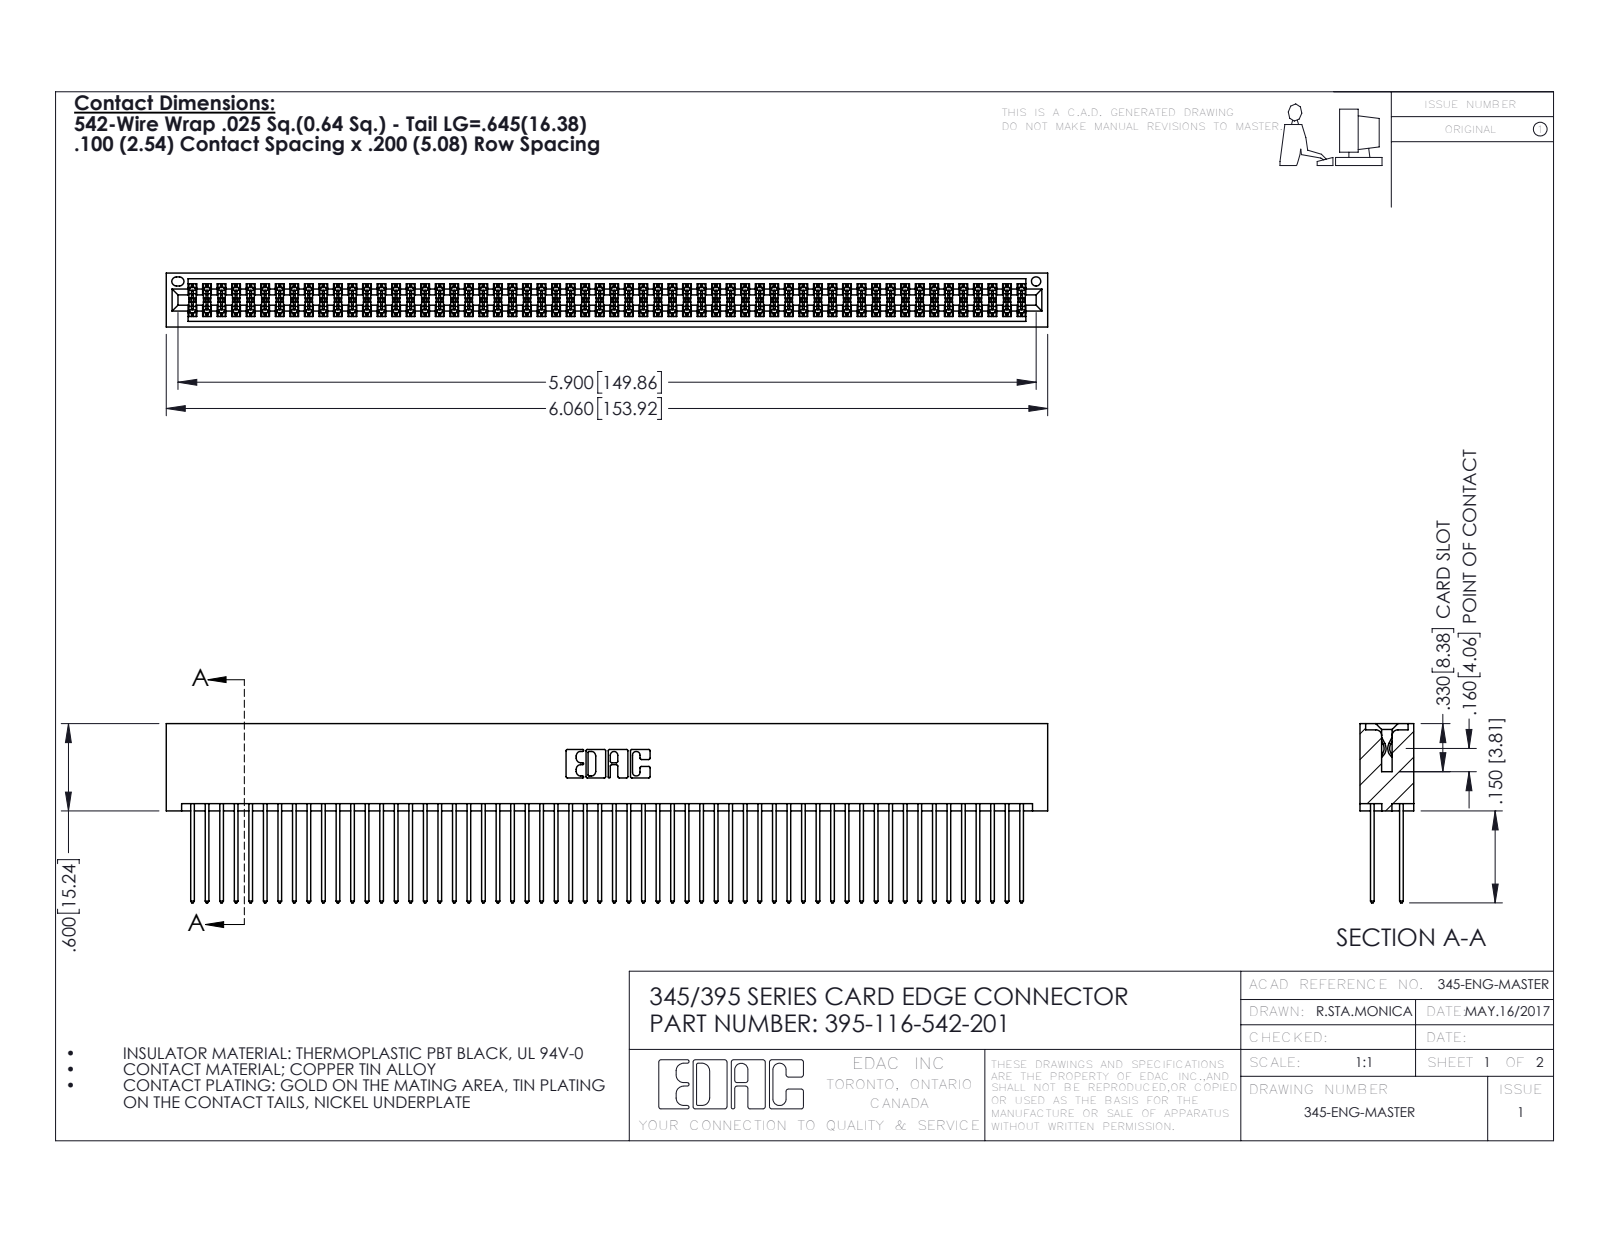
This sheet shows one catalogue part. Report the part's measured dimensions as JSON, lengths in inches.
{"part_name": "395-116-542-201; 345-292-001_345-293-142; 345 Part_No Mounting Lugs", "step_written_by": "SolidWorks 2016 (CONFIG_CONTROL_DESIGN)", "units": "inches", "bodies": {"solids": 117, "faces": 5918, "planar": 3904, "cylindrical": 2014, "other": 0}, "overall_size": [6.06, 1.232, 0.37], "volume_in3": 0.992, "surface_area_in2": 42.12, "round_holes": [[0.064, 1]], "partial_cylinders_radius": [[0.006, 174], [0.01, 116], [0.01, 22], [0.007, 6], [0.031, 6], [0.026, 3], [0.014, 2], [0.019, 2]], "face_to_face_distances": [0.298, 0.072, 0.2, 0.098, 0.272, 0.025, 0.225, 0.37, 0.175, 0.149]}
